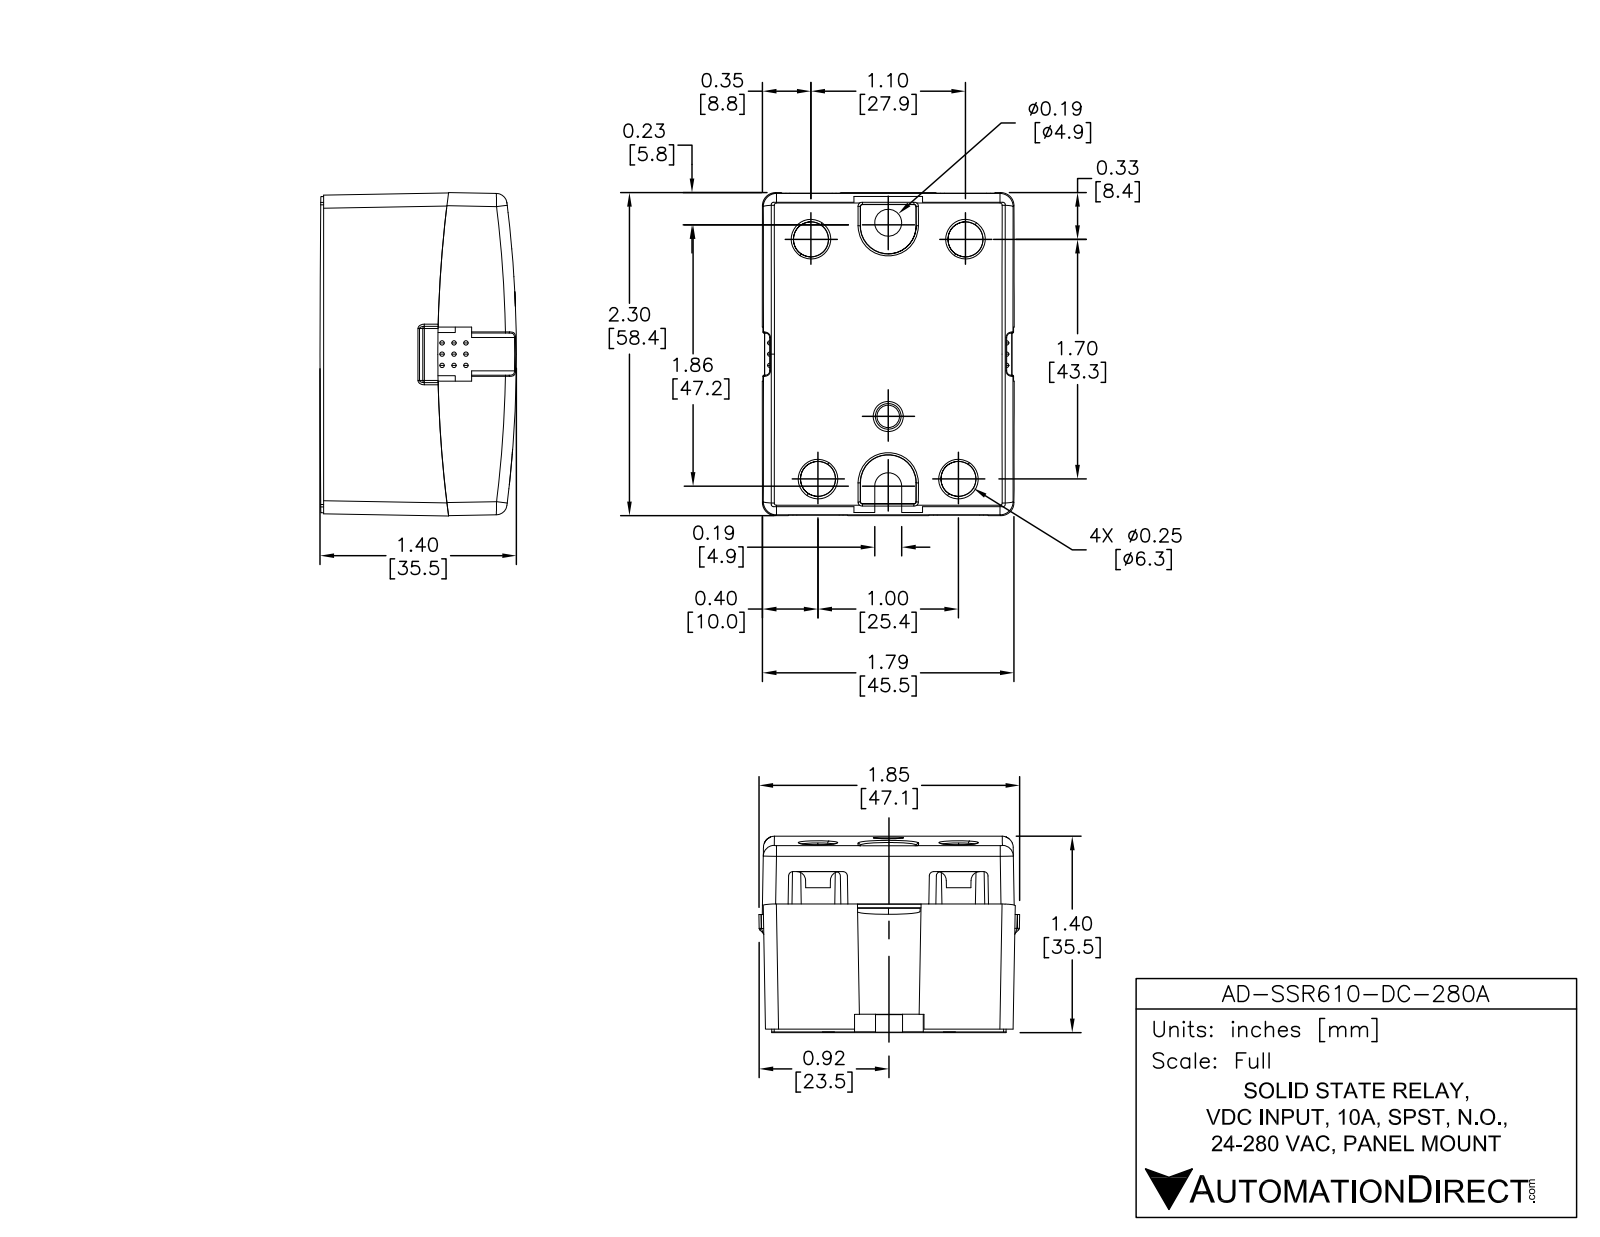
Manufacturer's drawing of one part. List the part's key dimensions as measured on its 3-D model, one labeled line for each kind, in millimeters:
Part name (STEP PRODUCT): AD-SSR610-DC-280A
STEP written by: SolidWorks 2013 (AUTOMOTIVE_DESIGN)
Units: millimetres
Bodies: 3 solids, 251 faces (145 planar, 95 cylindrical, 11 other)
Overall size (bounding box): 58.4 × 45.5 × 35.6
Volume: 84 230 mm³ · Surface area: 17 040 mm²
Round holes (diameter × count): ⌀6.4 ×4, ⌀4.8 ×1
Round bosses / shafts (diameter × count): ⌀10.2 ×2, ⌀8.9 ×2, ⌀7.6 ×2, ⌀6.4 ×2, ⌀5.1 ×2, ⌀5.1 ×2
Partial cylindrical surfaces — rounded edges, fillets, slot ends (radius × count): R0.8 ×6, R0.3 ×4, R1 ×4, R12.7 ×4, R4.9 ×2, R2.4 ×1, R12.7 ×1, R12.7 ×1
Main face-to-face distances: 45.5, 58.4, 29.6, 6.4, 23.3, 17, 26.9, 12.7, 45.7, 2
Hole centre spacings: 14.1, 14.4, 25.4, 27.9, 43.2, 43.2, 47.7, 47.7
